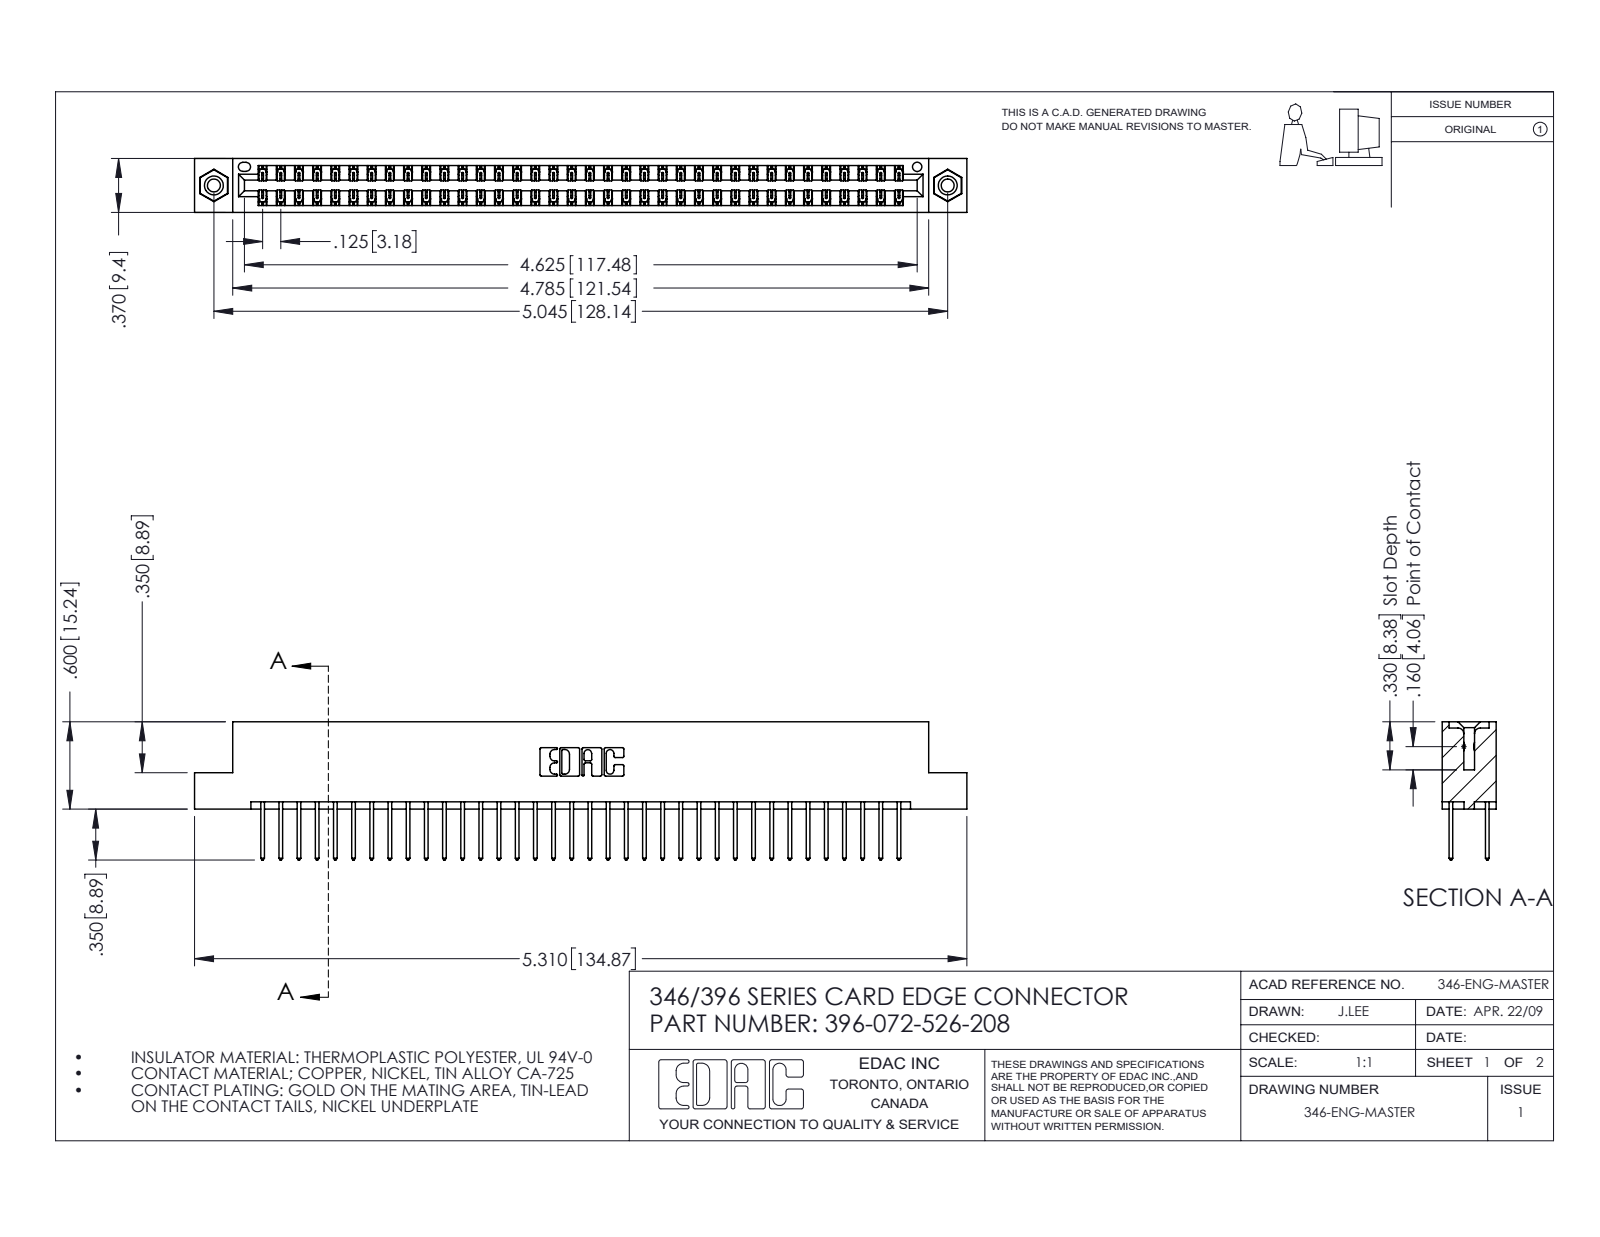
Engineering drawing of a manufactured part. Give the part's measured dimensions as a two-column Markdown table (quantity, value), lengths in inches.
| quantity | value |
| --- | --- |
| part name | 396-072-526-208; 345-250-001_345-250-003-102; 345-292-001_345-293-126; 346 Part_Flush Mounting Lugs - 0.156 Dia-TI |
| STEP written by | SolidWorks 2016 (CONFIG_CONTROL_DESIGN) |
| units | inches |
| bodies | 75 solids, 3926 faces (2628 planar, 1282 cylindrical, 16 other) |
| overall size | 5.31 × 0.95 × 0.37 |
| volume | 0.807 in³ |
| surface area | 28.86 in² |
| round holes (diameter × count) | 0.089 × 2, 0.125 × 2, 0.156 × 2, 0.064 × 1 |
| round bosses / shafts (diameter × count) | 0.155 × 2 |
| partial cylindrical surfaces (radius × count) | 0.006 × 108, 0.01 × 72, 0.01 × 22, 0.007 × 6, 0.031 × 6, 0.026 × 3, 0.014 × 2, 0.022 × 2 |
| main face-to-face distances | 0.048, 0.322, 0.25, 0.37, 0.072, 0.298, 0.025, 0.275, 0.148, 0.222 |
| hole center spacings | 0.246, 4.836, 5.045 |
